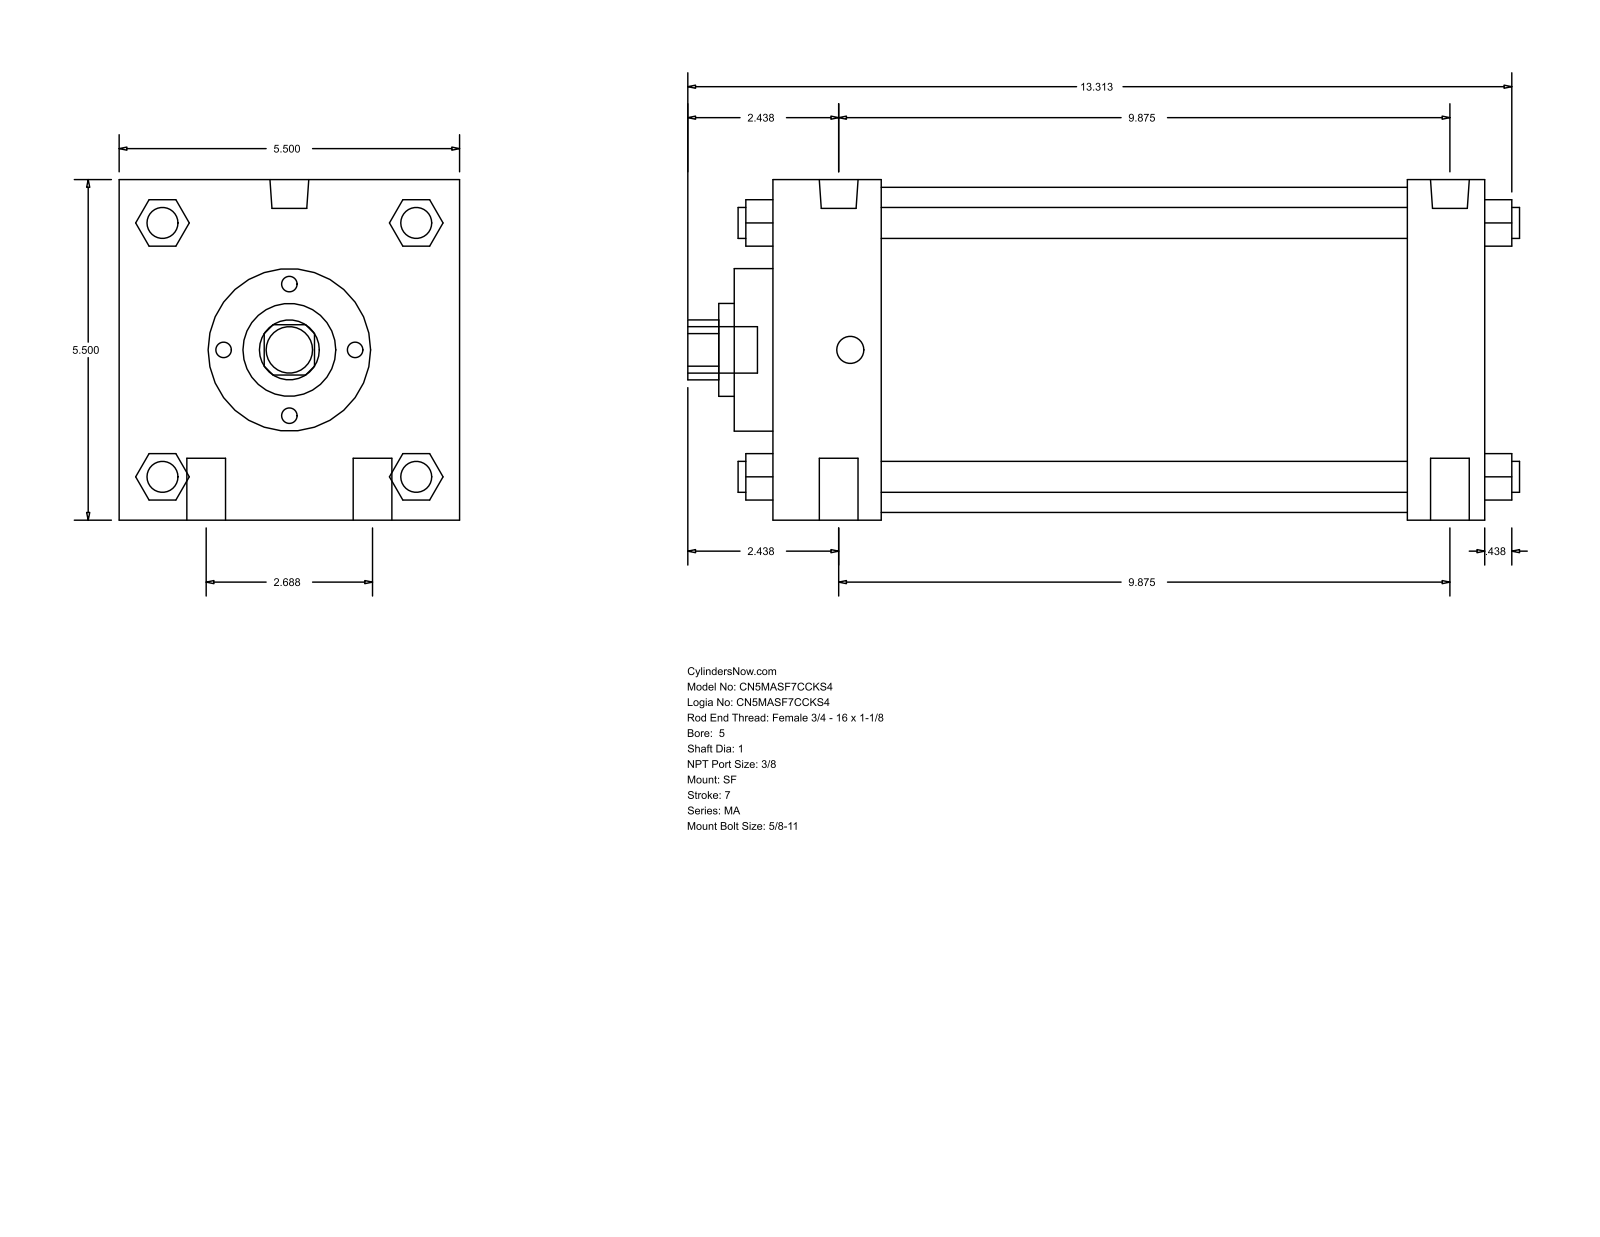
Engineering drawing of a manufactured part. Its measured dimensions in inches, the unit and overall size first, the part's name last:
Units: inches
Overall size (bounding box): 13.437 × 5.5 × 5.5
Round holes (diameter × count): ⌀1 ×1, ⌀1.5 ×1, ⌀2.625 ×1, ⌀5.25 ×1
Round bosses / shafts (diameter × count): ⌀0.625 ×4, ⌀0.5 ×4, ⌀0.627 ×2, ⌀0.437 ×2, ⌀0.75 ×1
Partial cylindrical surfaces — rounded edges, fillets, slot ends (radius × count): R0.484 ×1
Main face-to-face distances: 5.5, 11.5, 1.75, 10.25, 8.5, 9.75, 1.25, 0.625, 2.375, 10.875
Bodies: 0 solids, 126 faces (95 planar, 31 cylindrical, 0 other)
Part name (STEP PRODUCT): MA_SF__0500_1
STEP written by: GSSL Pune (CONFIG_CONTROL_DESIGN)
